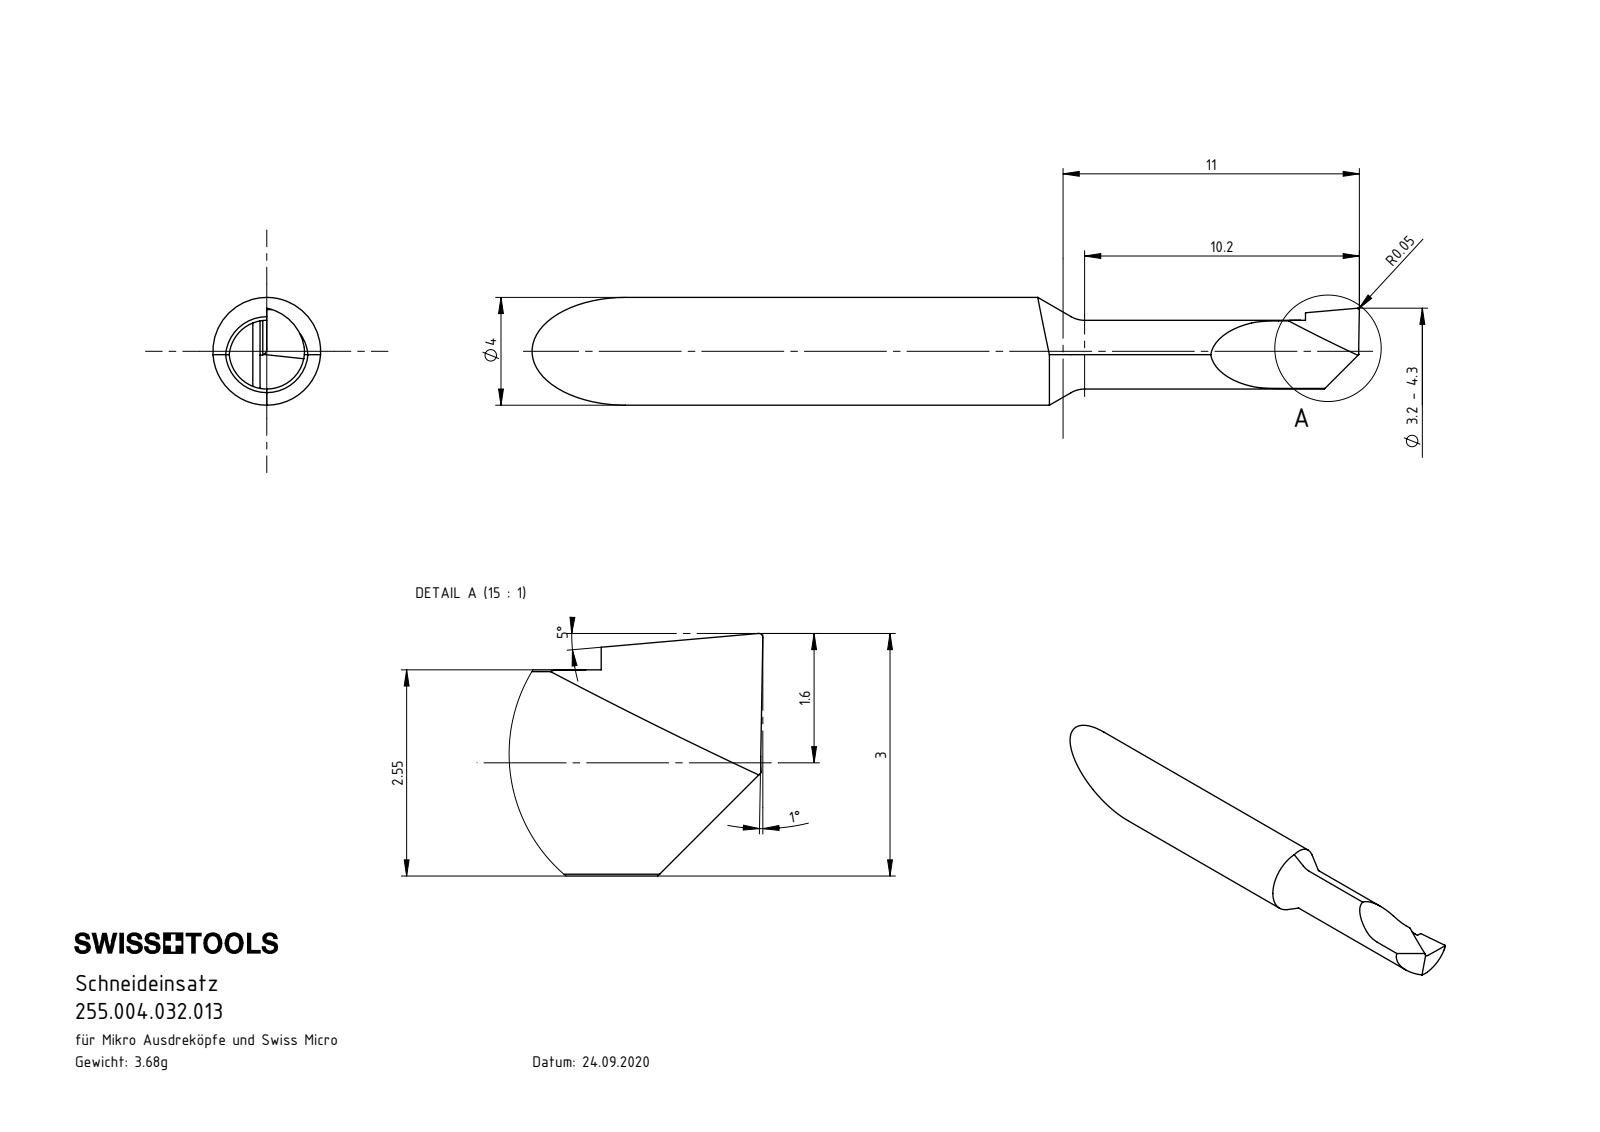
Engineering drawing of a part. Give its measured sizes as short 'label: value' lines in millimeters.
name: A04.0145.10.32.05_YR
written by: SolidWorks 2017 (AUTOMOTIVE_DESIGN)
unit: mm
bodies: 1 solid, 27 faces (8 planar, 6 cylindrical, 13 other)
size: 30.71 × 4 × 4
volume: 254 mm³; area: 320 mm²
bosses: 1× ⌀4
rounds: 2× R1.4, 1× R2
face distances: 12.08
